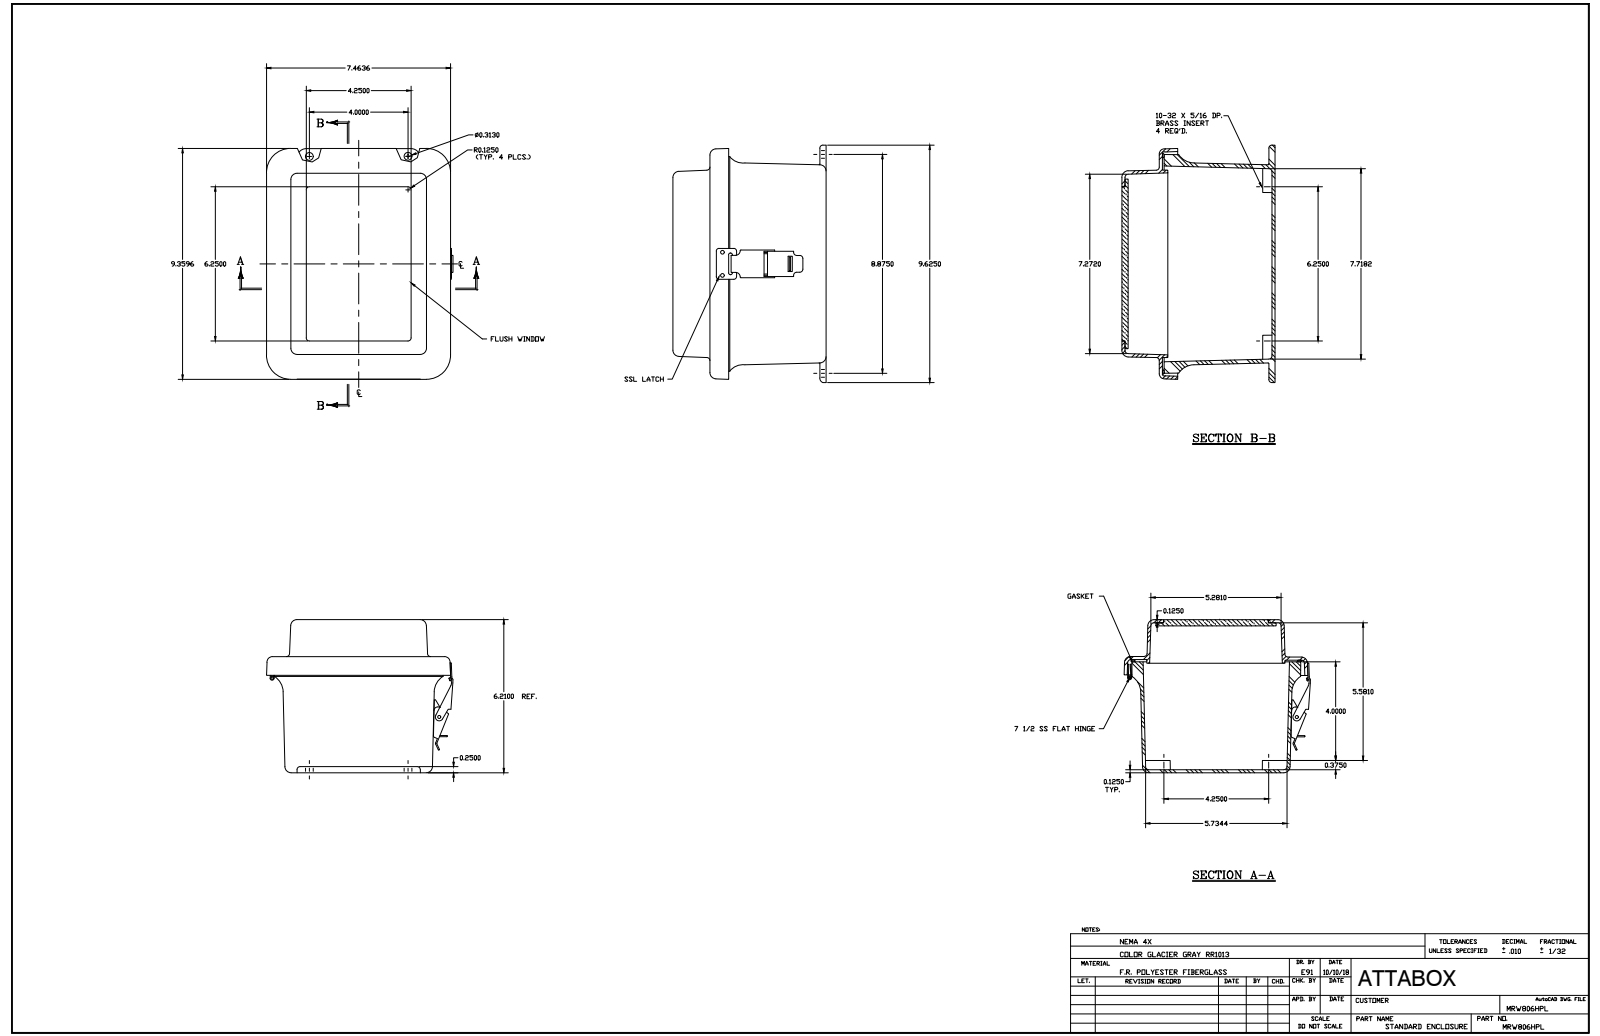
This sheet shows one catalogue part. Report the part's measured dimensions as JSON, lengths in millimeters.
{"part_name": "MRW806HPL", "step_written_by": "SolidWorks 2018 (AUTOMOTIVE_DESIGN)", "units": "millimeters", "bodies": {"solids": 26, "faces": 772, "planar": 316, "cylindrical": 304, "other": 152}, "overall_size": [244.5, 191.8, 157.9], "volume_mm3": 866400, "surface_area_mm2": 459000, "round_holes": [[3.6, 12], [3.3, 6], [3.9, 5], [4, 5], [2.6, 4], [5.5, 4], [3.3, 2], [3.4, 2], [2.2, 1], [2.2, 1], [3.4, 1], [9.5, 1]], "round_bosses_or_shafts": [[6.4, 5], [3.2, 5], [6.9, 4], [3.2, 4], [7.6, 1], [4.3, 1], [3.9, 1], [3, 1]], "partial_cylinders_radius": [[3.2, 28], [0.8, 20], [6.4, 16], [0.4, 12], [1.1, 8], [0.8, 6], [0.6, 4], [1.5, 4]], "face_to_face_distances": [3.2, 3.2, 151.5, 6.4, 113, 157.9, 154.7, 38.5, 148.3, 116.2], "hole_center_spacings": [88.9, 6.4, 19.1, 23.8, 33.7, 133.9, 184.1, 225.1]}
